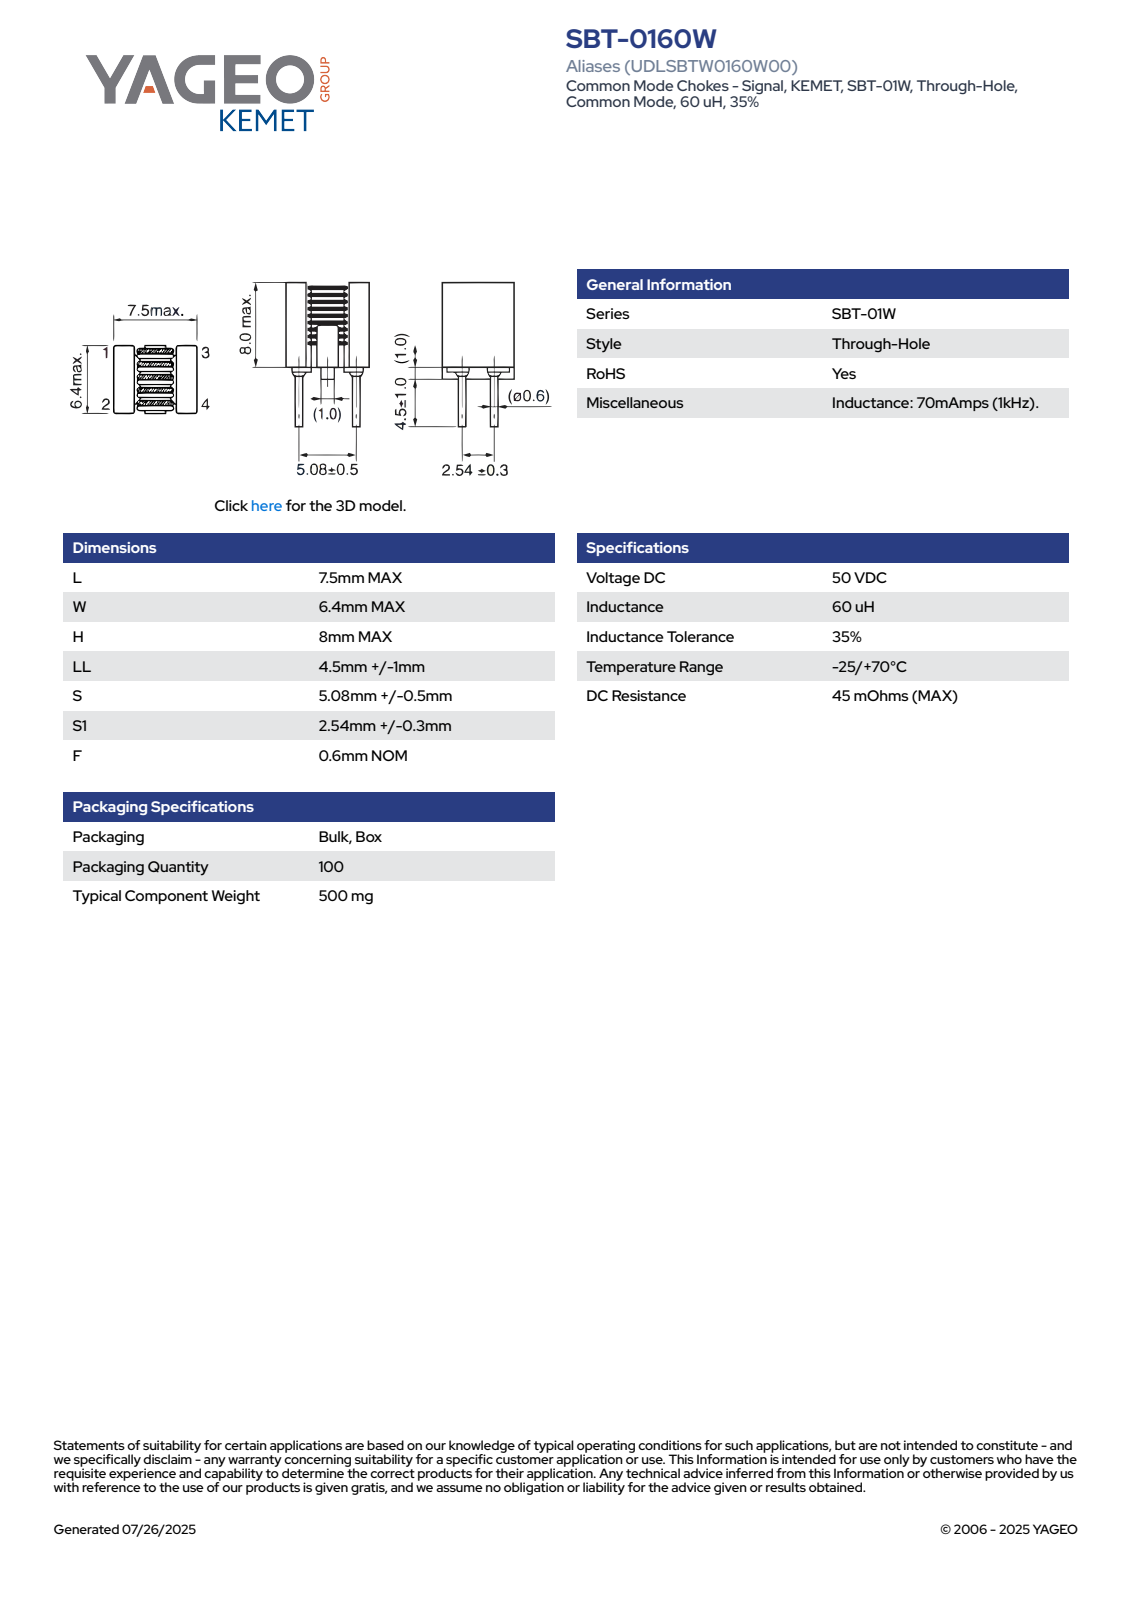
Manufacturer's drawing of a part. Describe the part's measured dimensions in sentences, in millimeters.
The part is named "IFC_NTSBT01W_L7.5W6.4H8". Its 3-D file was written by "SolidWorks 2014 (AUTOMOTIVE_DESIGN)". It is 1 solid with 162 faces: 89 planar, 51 cylindrical and 22 other. Overall it measures 14.51 by 7.5 by 6.4 millimeters. Its volume is 293 cubic millimeters and its surface area 479 square millimeters. Round bosses or shafts: 4 of diameter 0.6, 1 of diameter 4.61. Partial cylindrical surfaces (rounded edges, fillets, slot ends): 32 of radius 0.2. The main face-to-face distances are 1.68, 5.82, 7.5, 4.14, 2.73, 4.77, 1.05, 3.09, 6.4, 5.25.
